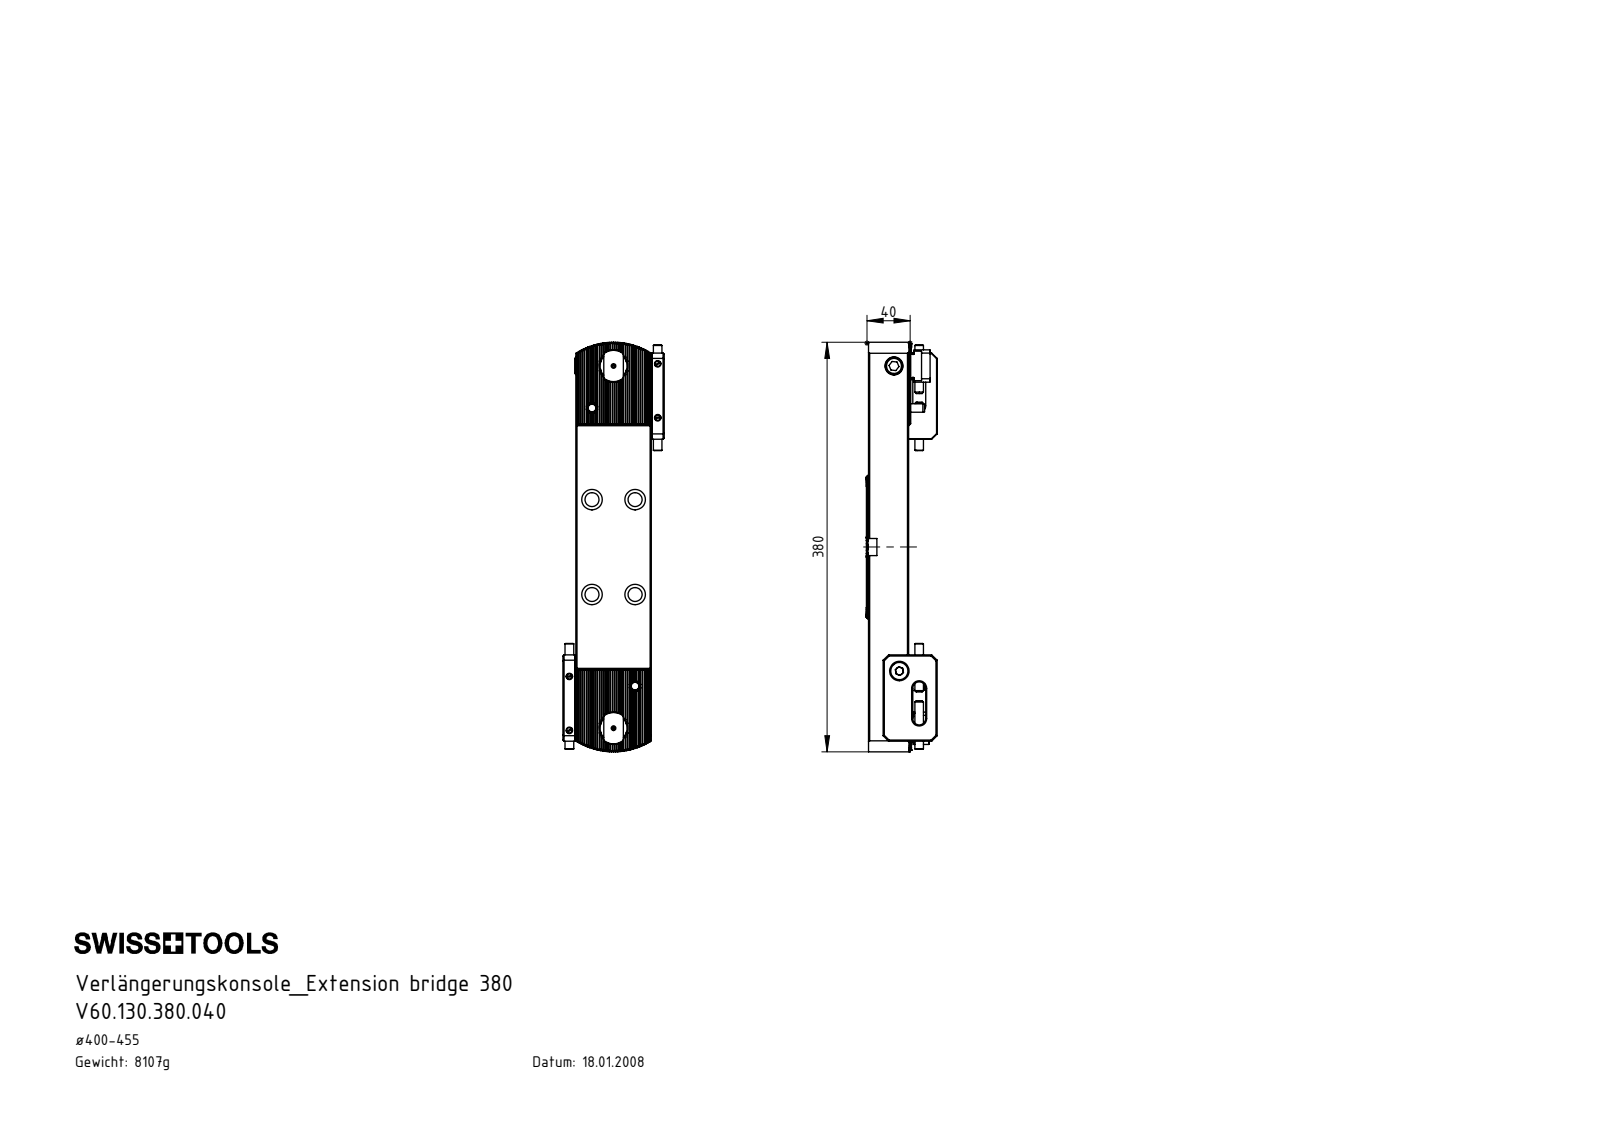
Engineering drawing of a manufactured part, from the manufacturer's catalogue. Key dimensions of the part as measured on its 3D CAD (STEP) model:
Part name (STEP PRODUCT): VK1-ER2.201.010_A_vorgespannt; VK1-ER2.201.010_A_gespannt; VK1-ER1.001.030_A; Ko1.VK1.380.040 (+8 more)
STEP written by: SolidWorks 2017 (AUTOMOTIVE_DESIGN)
Units: millimetres
Bodies: 27 solids, 1255 faces (842 planar, 260 cylindrical, 153 other)
Overall size (bounding box): 380 × 94 × 65.58
Volume: 1 039 000 mm³ · Surface area: 166 217 mm²
Round holes (diameter × count): ⌀5 ×4, ⌀6 ×4, ⌀6.8 ×4, ⌀13 ×4, ⌀19 ×4, ⌀2 ×2, ⌀8 ×2, ⌀8.5 ×2, ⌀10.5 ×2, ⌀11 ×2, ⌀14 ×2, ⌀18 ×2
Round bosses / shafts (diameter × count): ⌀16 ×4, ⌀6 ×4, ⌀10 ×2, ⌀8 ×2
Partial cylindrical surfaces — rounded edges, fillets, slot ends (radius × count): R0.14 ×66, R2 ×8, R6 ×4, R12.3 ×2, R15 ×2, R65 ×2, R7.95 ×1
Main face-to-face distances: 37.16, 70, 12, 82, 1.73, 8.66, 3.46, 6.93, 0.5, 41.57
Hole centre spacings: 125.6, 212.94, 336, 7.9, 18.55, 19.61, 34.53, 35.09
